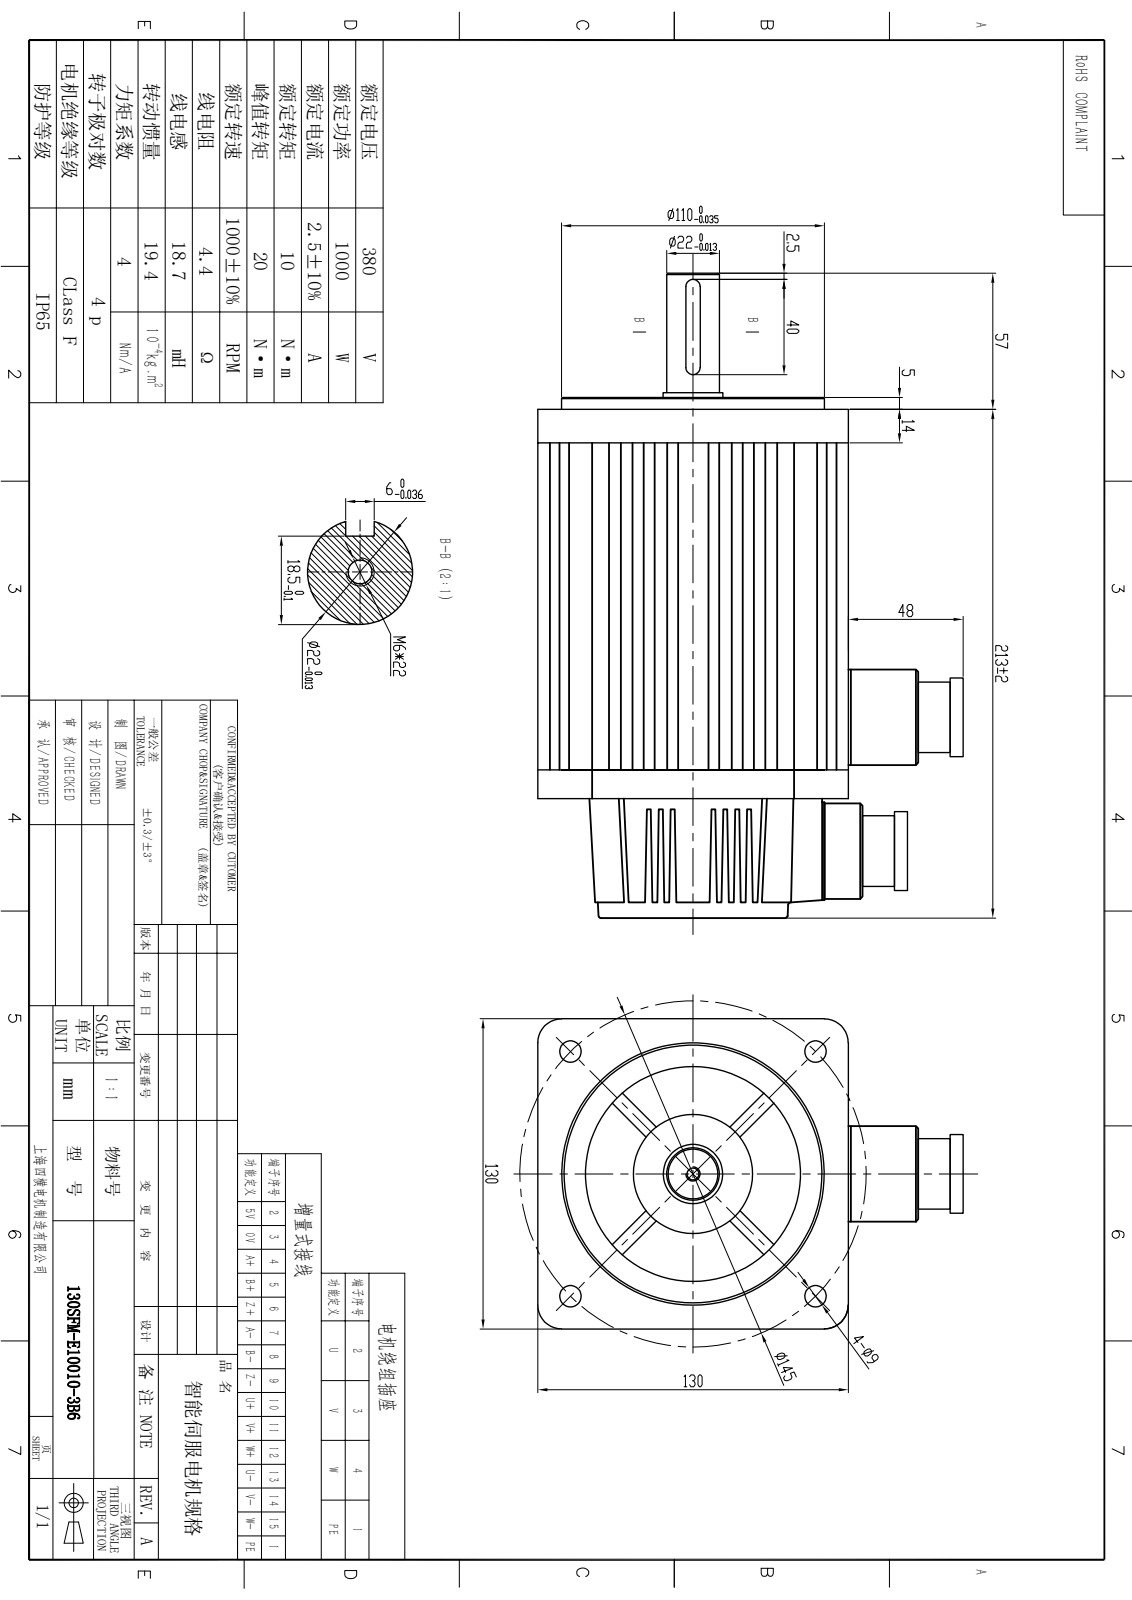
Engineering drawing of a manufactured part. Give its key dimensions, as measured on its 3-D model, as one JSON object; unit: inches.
{"part_name": "130SFM-E10010-3B6", "step_written_by": "SolidWorks 2020 (CONFIG_CONTROL_DESIGN)", "units": "inches", "bodies": {"solids": 10, "faces": 1040, "planar": 395, "cylindrical": 277, "other": 368}, "overall_size": [10.63, 6.772, 5.118], "volume_in3": 173.4, "surface_area_in2": 405.7, "round_holes": [[0.098, 8], [0.256, 4], [0.354, 4], [0.433, 4], [0.984, 2], [0.197, 1], [3.898, 1]], "round_bosses_or_shafts": [[0.059, 15], [0.394, 4], [0.236, 4], [0.157, 3], [1.181, 2], [4.331, 1], [3.15, 1], [2.756, 1]], "partial_cylinders_radius": [[0.02, 76], [0.118, 10], [0.079, 8], [0.394, 4], [1.959, 1], [2.539, 1]], "face_to_face_distances": [5.276, 0.472, 5.748, 5.118, 0.079, 5.039, 6.299, 0.551, 5.827, 0.827], "hole_center_spacings": [0.78, 1.058, 1.102, 1.496, 2.677, 3.786, 4.037, 0.652]}
